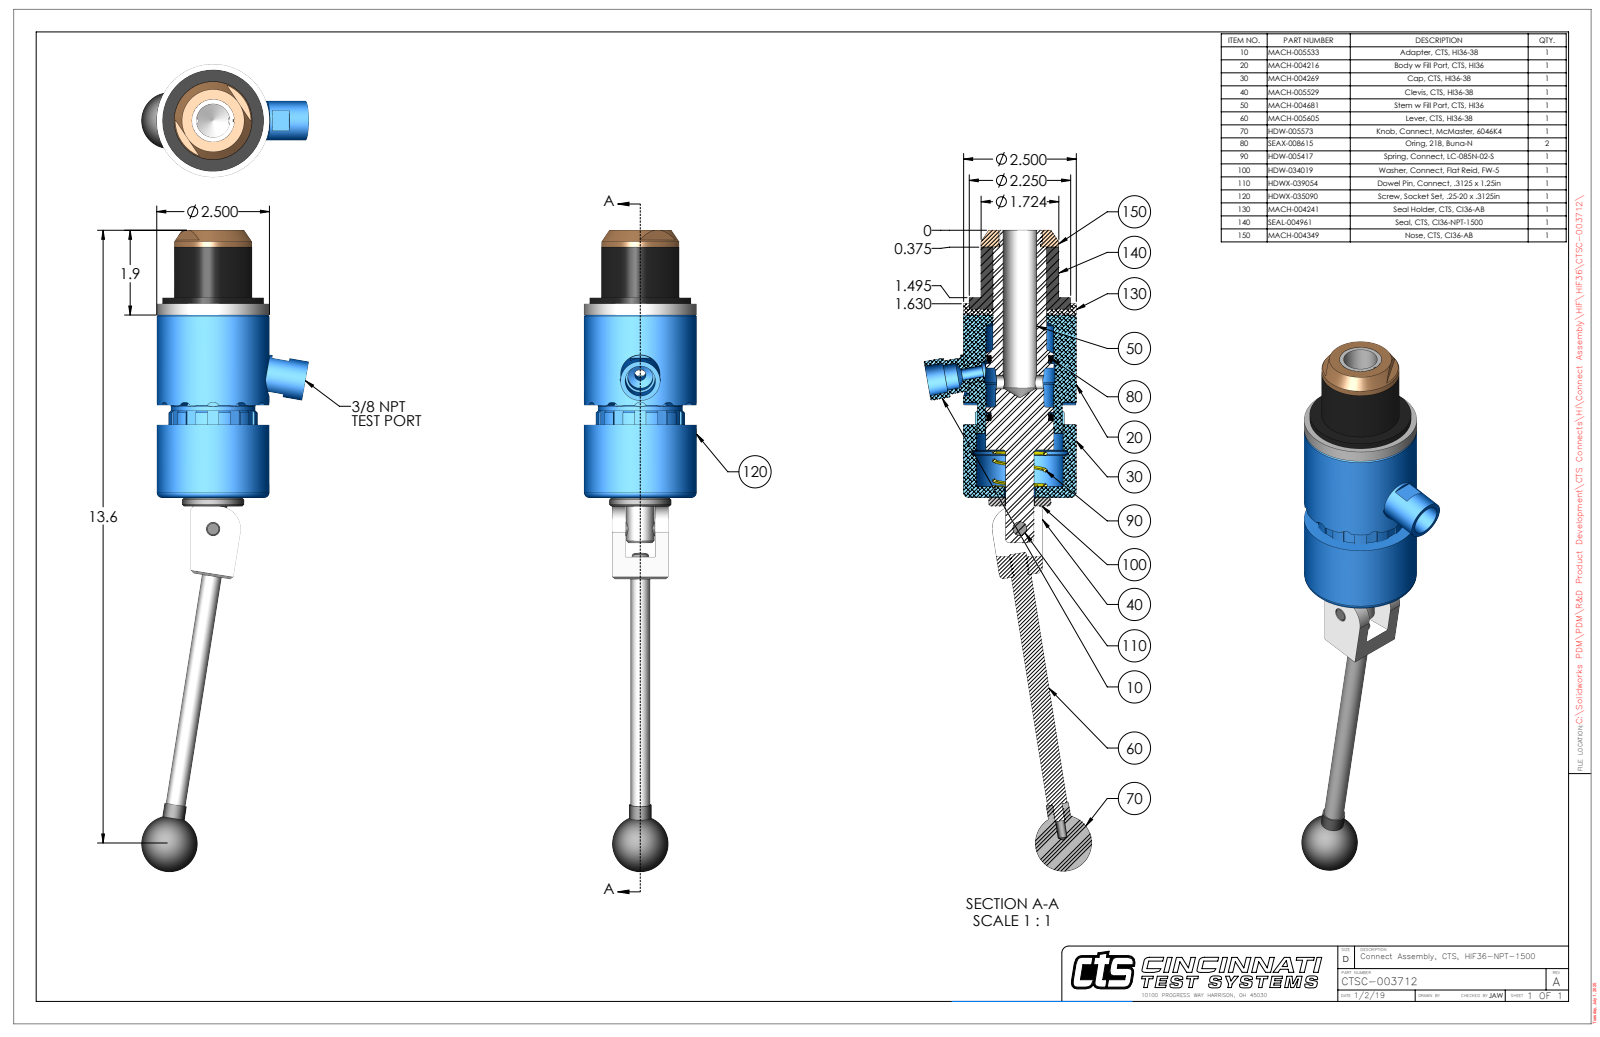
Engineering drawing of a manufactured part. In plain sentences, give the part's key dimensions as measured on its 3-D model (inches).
The part is named "CTSC-003712". Its 3-D file was written by "SolidWorks 2023 (AUTOMOTIVE_DESIGN)". It is 9 solids with 392 faces: 167 planar, 148 cylindrical and 77 other. Overall it measures 14.215 by 3.716 by 2.5 inches. Its volume is 26.37 cubic inches and its surface area 133.4 square inches. Round holes: 2 of diameter 0.201, 1 of diameter 0.15, 1 of diameter 0.25, 1 of diameter 0.311, 1 of diameter 0.312, 1 of diameter 0.313, 1 of diameter 0.314, 1 of diameter 0.562, 1 of diameter 0.656, 1 of diameter 0.696, 1 of diameter 0.75, 1 of diameter 0.922. Round bosses or shafts: 1 of diameter 2.5, 1 of diameter 2.25, 1 of diameter 1.875, 1 of diameter 1.73, 1 of diameter 1.724, 1 of diameter 1.38, 1 of diameter 1.186, 1 of diameter 1. Partial cylindrical surfaces (rounded edges, fillets, slot ends): 12 of radius 0.12, 2 of radius 0.029, 1 of radius 0.19, 1 of radius 0.195, 1 of radius 0.444, 1 of radius 0.47, 1 of radius 0.5, 1 of radius 0.961. The main face-to-face distances are 0.125, 4.05, 4.175, 5.555, 1.505, 1.38, 0.297, 0.953, 1.62, 2.43. The hole center spacings are 0.74, 2.118, 2.858.
